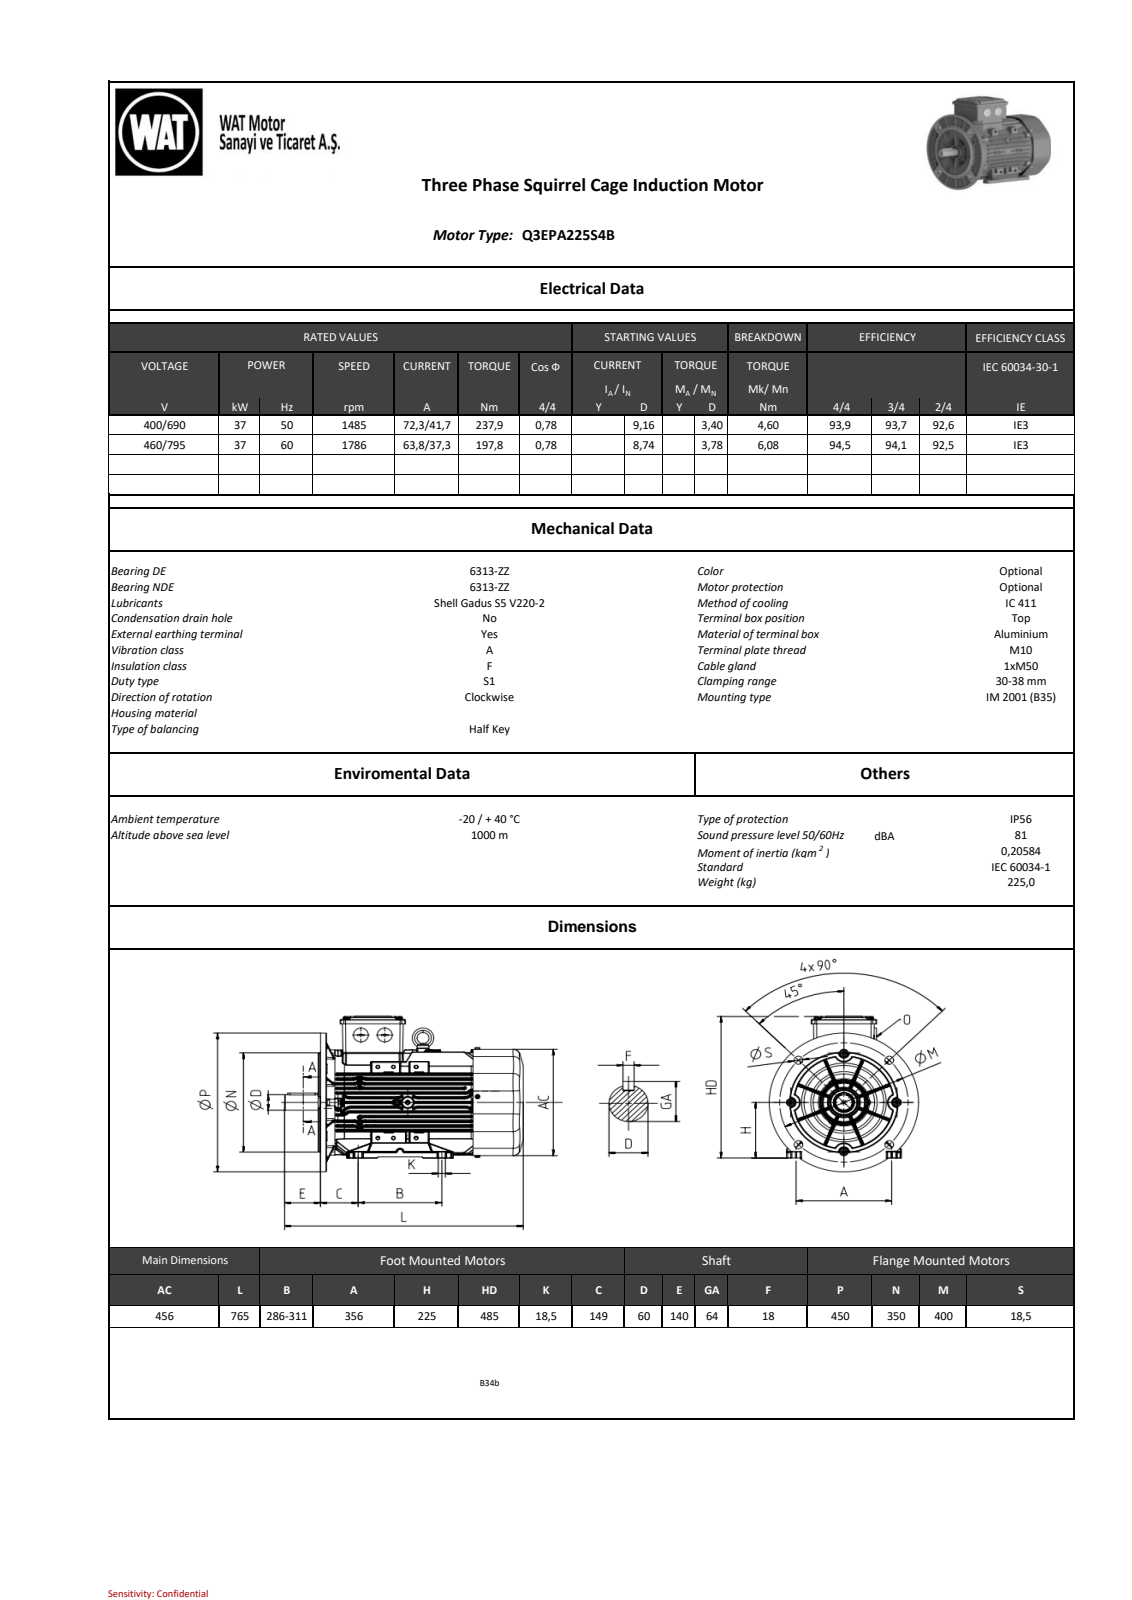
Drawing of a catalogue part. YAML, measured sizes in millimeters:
part_name: "AB_objects"
step_written_by: "SIEMENS PLM Software NX2206.8101 (AUTOMOTIVE_DESIGN)"
units: millimeters
bodies: {solids: 0, faces: 14653, planar: 6453, cylindrical: 2760, other: 5440}
overall_size: [765, 507.5, 450]
round_holes:
  - {diameter: 10.5, count: 8}
  - {diameter: 19, count: 8}
  - {diameter: 0.7, count: 6}
  - {diameter: 6, count: 5}
  - {diameter: 7.5, count: 5}
  - {diameter: 4.3, count: 4}
  - {diameter: 5.5, count: 4}
  - {diameter: 6.5, count: 4}
  - {diameter: 8.38, count: 4}
  - {diameter: 19.5, count: 4}
  - {diameter: 4, count: 3}
  - {diameter: 5, count: 3}
round_bosses_or_shafts:
  - {diameter: 10, count: 6}
  - {diameter: 16.5, count: 4}
  - {diameter: 16, count: 4}
  - {diameter: 5.85, count: 3}
  - {diameter: 58, count: 2}
  - {diameter: 55.1, count: 2}
  - {diameter: 52.3, count: 2}
  - {diameter: 52.2, count: 2}
partial_cylinders:
  - {radius: 1, count: 619}
  - {radius: 2, count: 444}
  - {radius: 0.2, count: 332}
  - {radius: 0.5, count: 154}
  - {radius: 5, count: 81}
  - {radius: 2.5, count: 76}
  - {radius: 3, count: 48}
  - {radius: 4, count: 48}
face_to_face_distances: [189.81, 15.53, 169.04, 20.77, 14.83, 184.57, 5.24, 24.63, 150.23, 39.58]
hole_center_spacings: [7.4, 156, 146.34, 282.85, 68.18, 82.67, 200.01, 231.52]
